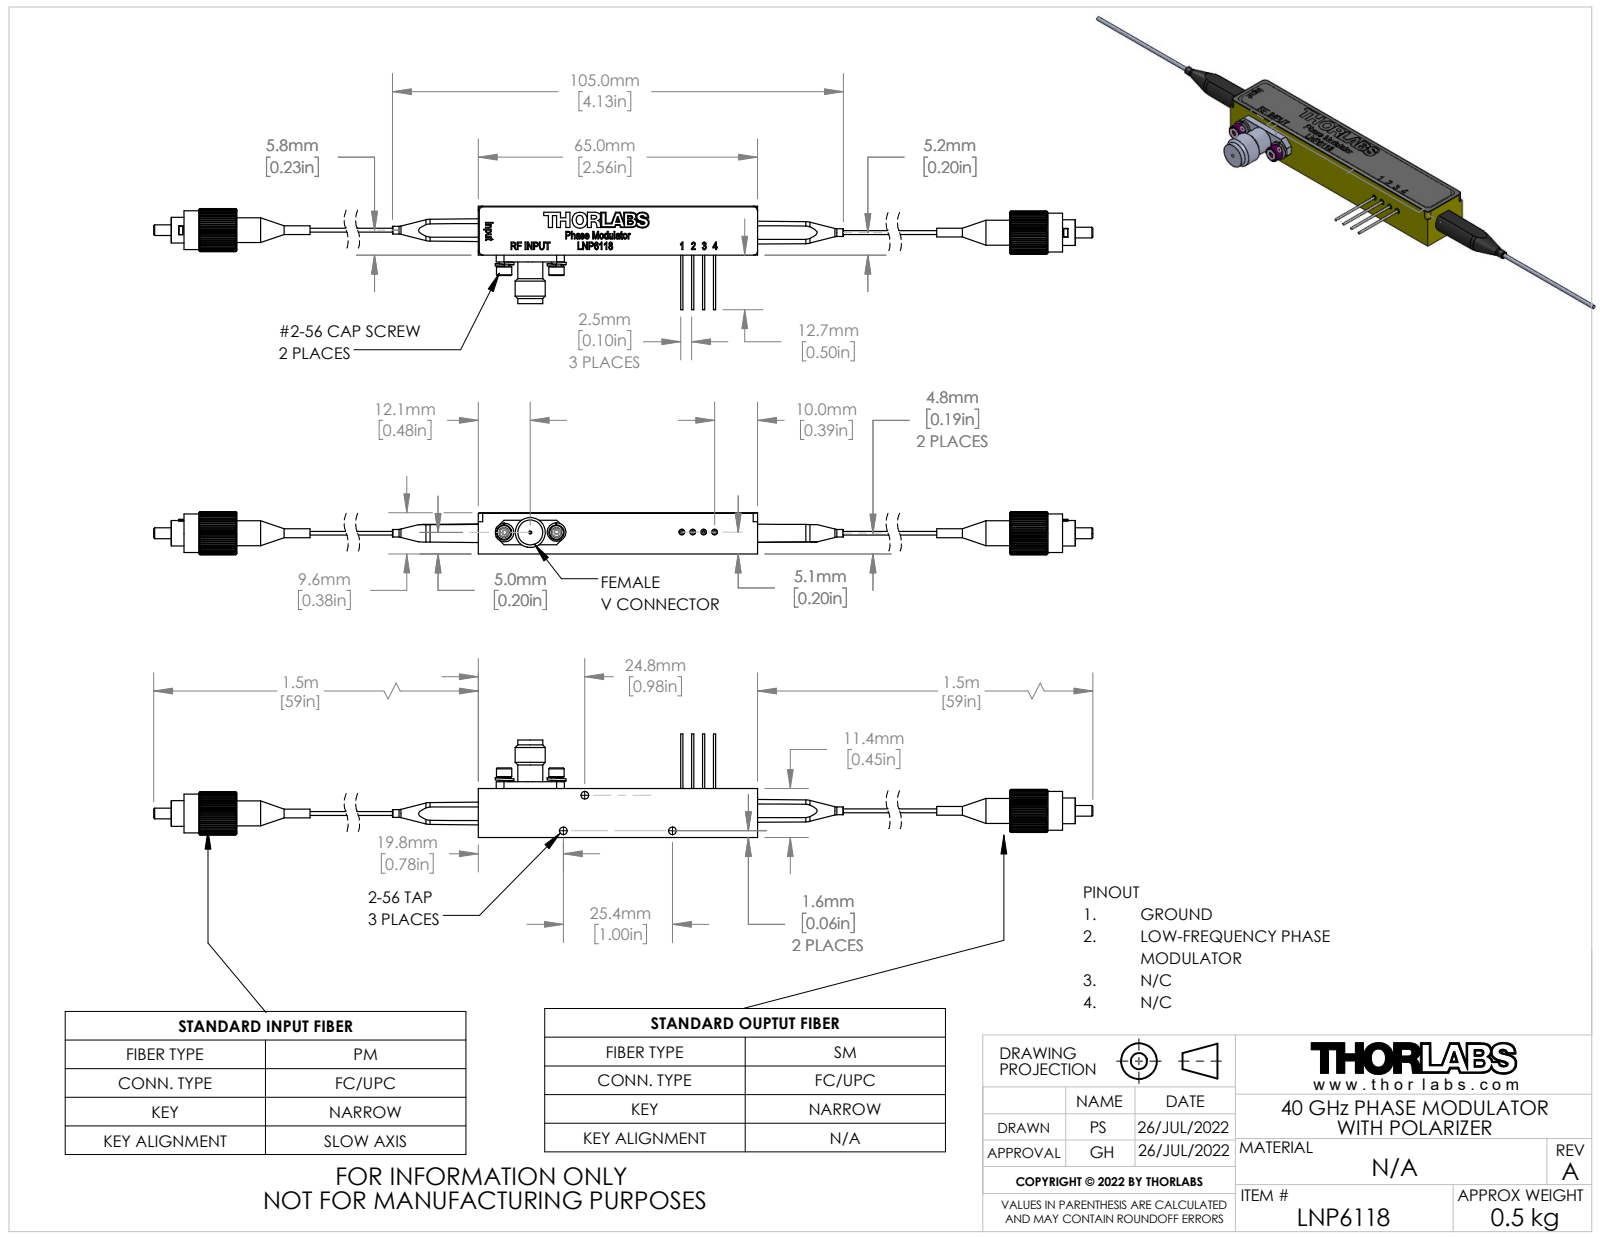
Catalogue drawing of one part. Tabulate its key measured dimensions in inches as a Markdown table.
| quantity | value |
| --- | --- |
| part name | QTN045767-E0W |
| STEP written by | SolidWorks 2018 (CONFIG_CONTROL_DESIGN) |
| units | inches |
| bodies | 0 solids, 426 faces (253 planar, 45 cylindrical, 128 other) |
| overall size | 6.055 × 0.949 × 0.379 |
| round holes (diameter × count) | 0.07 × 3, 0.028 × 1 |
| round bosses / shafts (diameter × count) | 0.02 × 4, 0.14 × 2, 0.086 × 2, 0.071 × 2, 0.035 × 2, 0.276 × 1, 0.228 × 1 |
| partial cylindrical surfaces (radius × count) | 0.039 × 4, 0.035 × 3 |
| main face-to-face distances | 0.379, 0.449, 0.374, 0.374, 2.559, 0.378, 0.063, 0.511, 0.382, 0.445 |
| hole center spacings | 0.381, 0.867, 1 |
